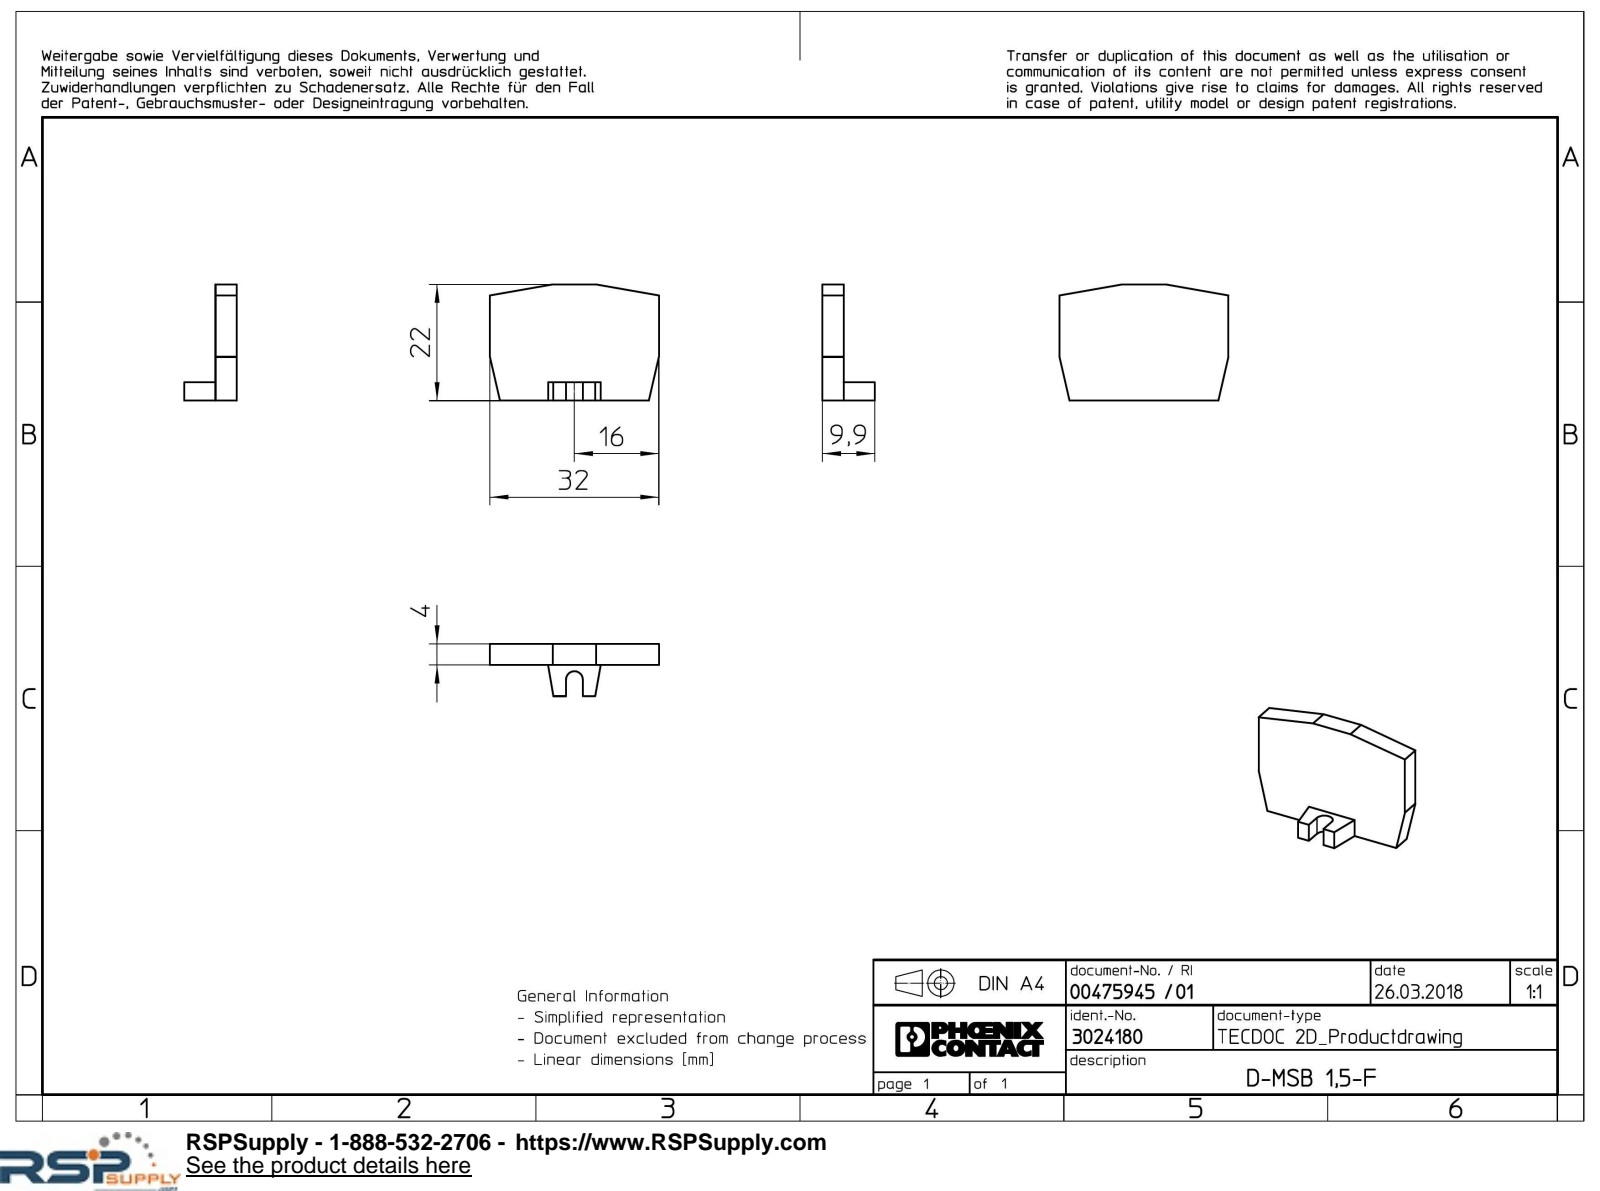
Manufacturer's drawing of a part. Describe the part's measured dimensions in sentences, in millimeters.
The part is named "D_MSB_1.5_F-select". Its 3-D file was written by "Creo Elements/Direct Modeling 18.1I 14-Aug-2016 (C) Parametric Technology GmbH (AUTOMOTIVE_DESIGN)". It is 1 solid with 18 faces: 17 planar, 1 cylindrical and 0 other. Overall it measures 32 by 22 by 9.9 millimeters. Its volume is 2 789 cubic millimeters and its surface area 1 870 square millimeters. Partial cylindrical surfaces (rounded edges, fillets, slot ends): 1 of radius 1.6. The main face-to-face distances are 4, 32, 3.5, 22, 18.5, 14.4, 17.6, 9.9, 5.9, 3.2.
